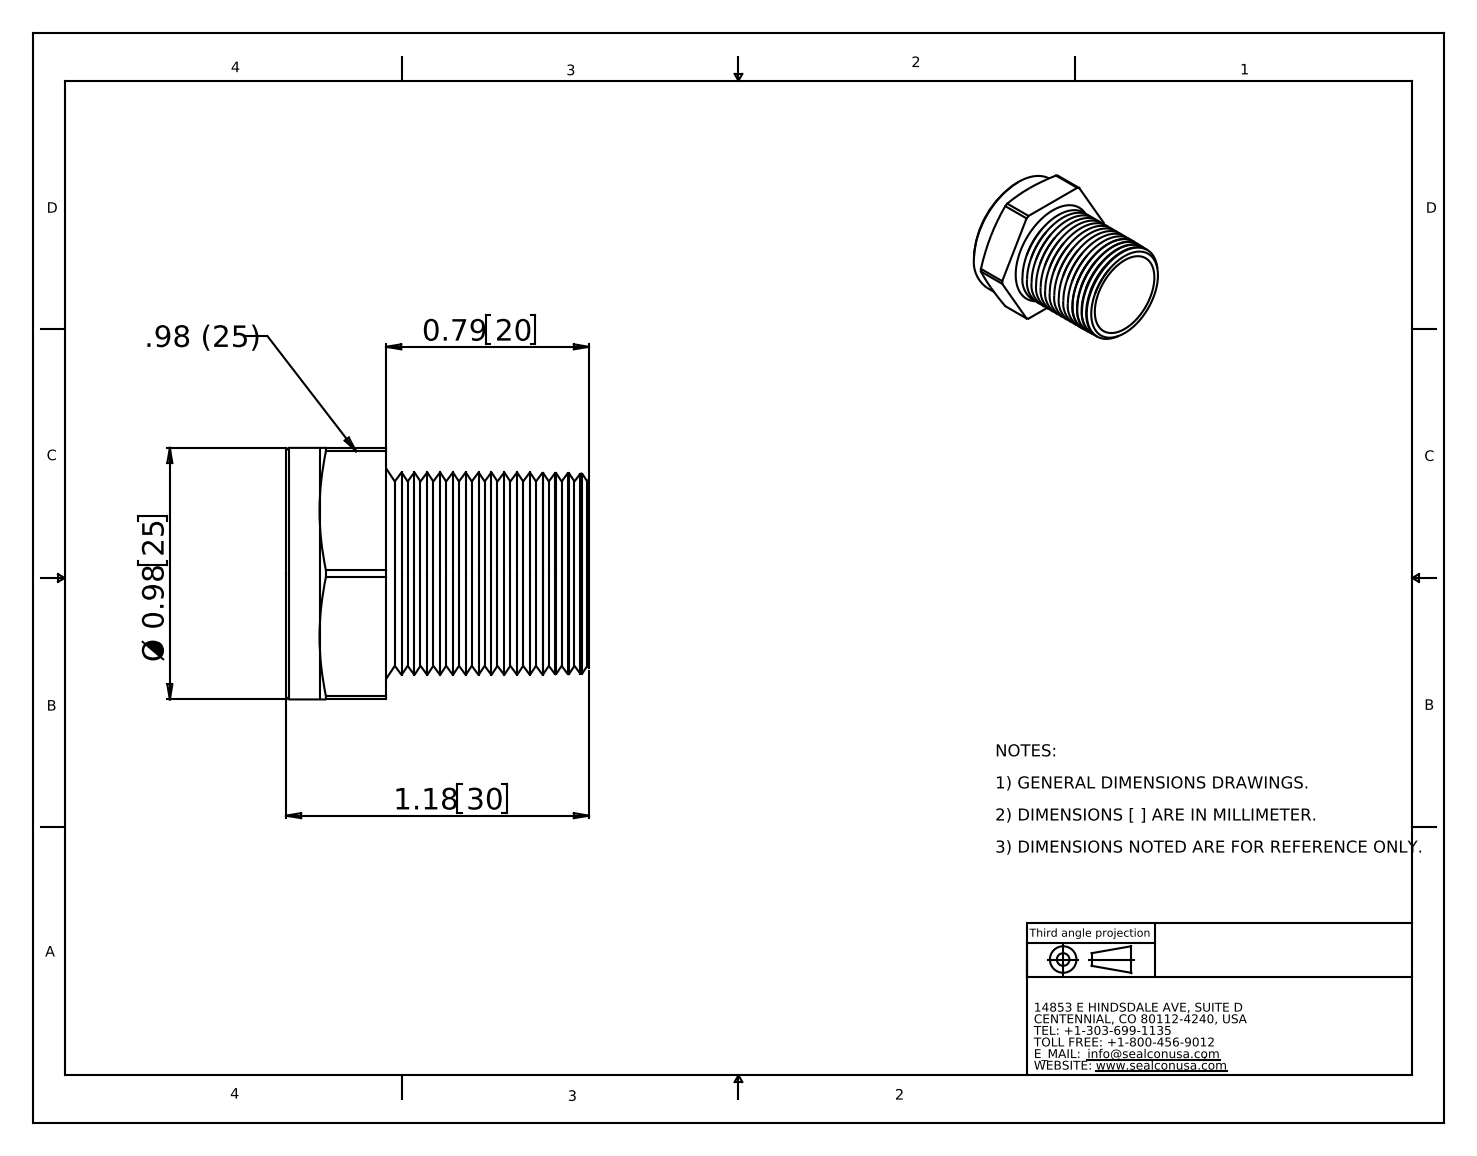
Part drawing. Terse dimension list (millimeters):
name: AT-1220-BR
written by: SolidWorks 2008 (CONFIG_CONTROL_DESIGN)
unit: mm
bodies: 1 solid, 127 faces (11 planar, 13 cylindrical, 103 other)
size: 30 × 28.4 × 24.9
volume: 3 650 mm³; area: 5 480 mm²
holes: 1× ⌀16.7, 1× ⌀20.8
bosses: 1× ⌀24.9
rounds: 1× R14.2
face distances: 24.9, 9.9, 1.5, 8.4, 4.5, 3, 5.4, 20.1, 21.6, 24.6
